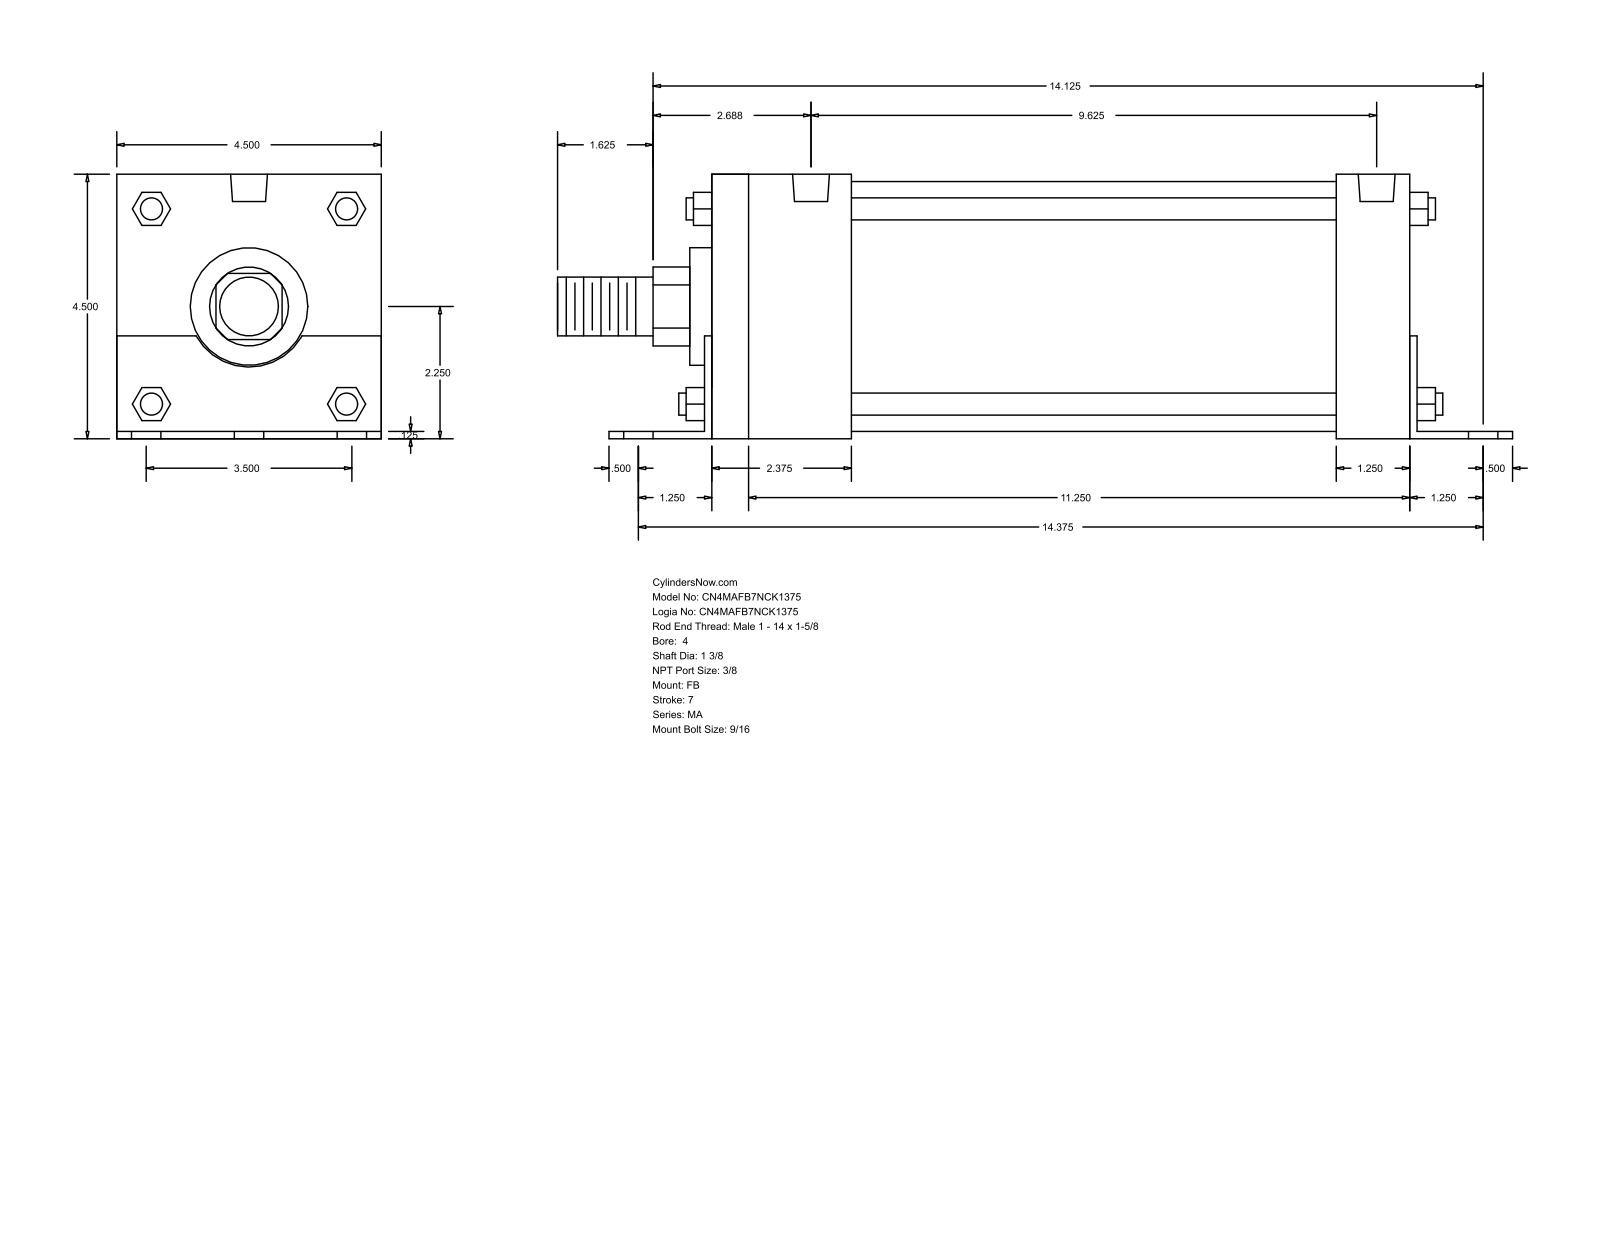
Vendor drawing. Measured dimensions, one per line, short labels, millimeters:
name: MA_FB__0400_1.375
written by: GSSL Pune (CONFIG_CONTROL_DESIGN)
unit: mm
bodies: 0 solids, 140 faces (105 planar, 35 cylindrical, 0 other)
size: 412.75 × 114.35 × 114.3
holes: 6× ⌀14.29, 4× ⌀11.11, 2× ⌀15.93
bosses: 4× ⌀9.53, 1× ⌀107.95, 1× ⌀50.8, 1× ⌀34.92, 1× ⌀25.4
rounds: 1× R17.06, 1× R26.16
face distances: 114.3, 3.17, 114.35, 3.12, 111.18, 301.62, 3.18, 304.8, 34.93, 304.79
hole spacings: 44.45, 367.82, 365.12, 63.99, 67.49, 86.85, 88.9, 90.98
